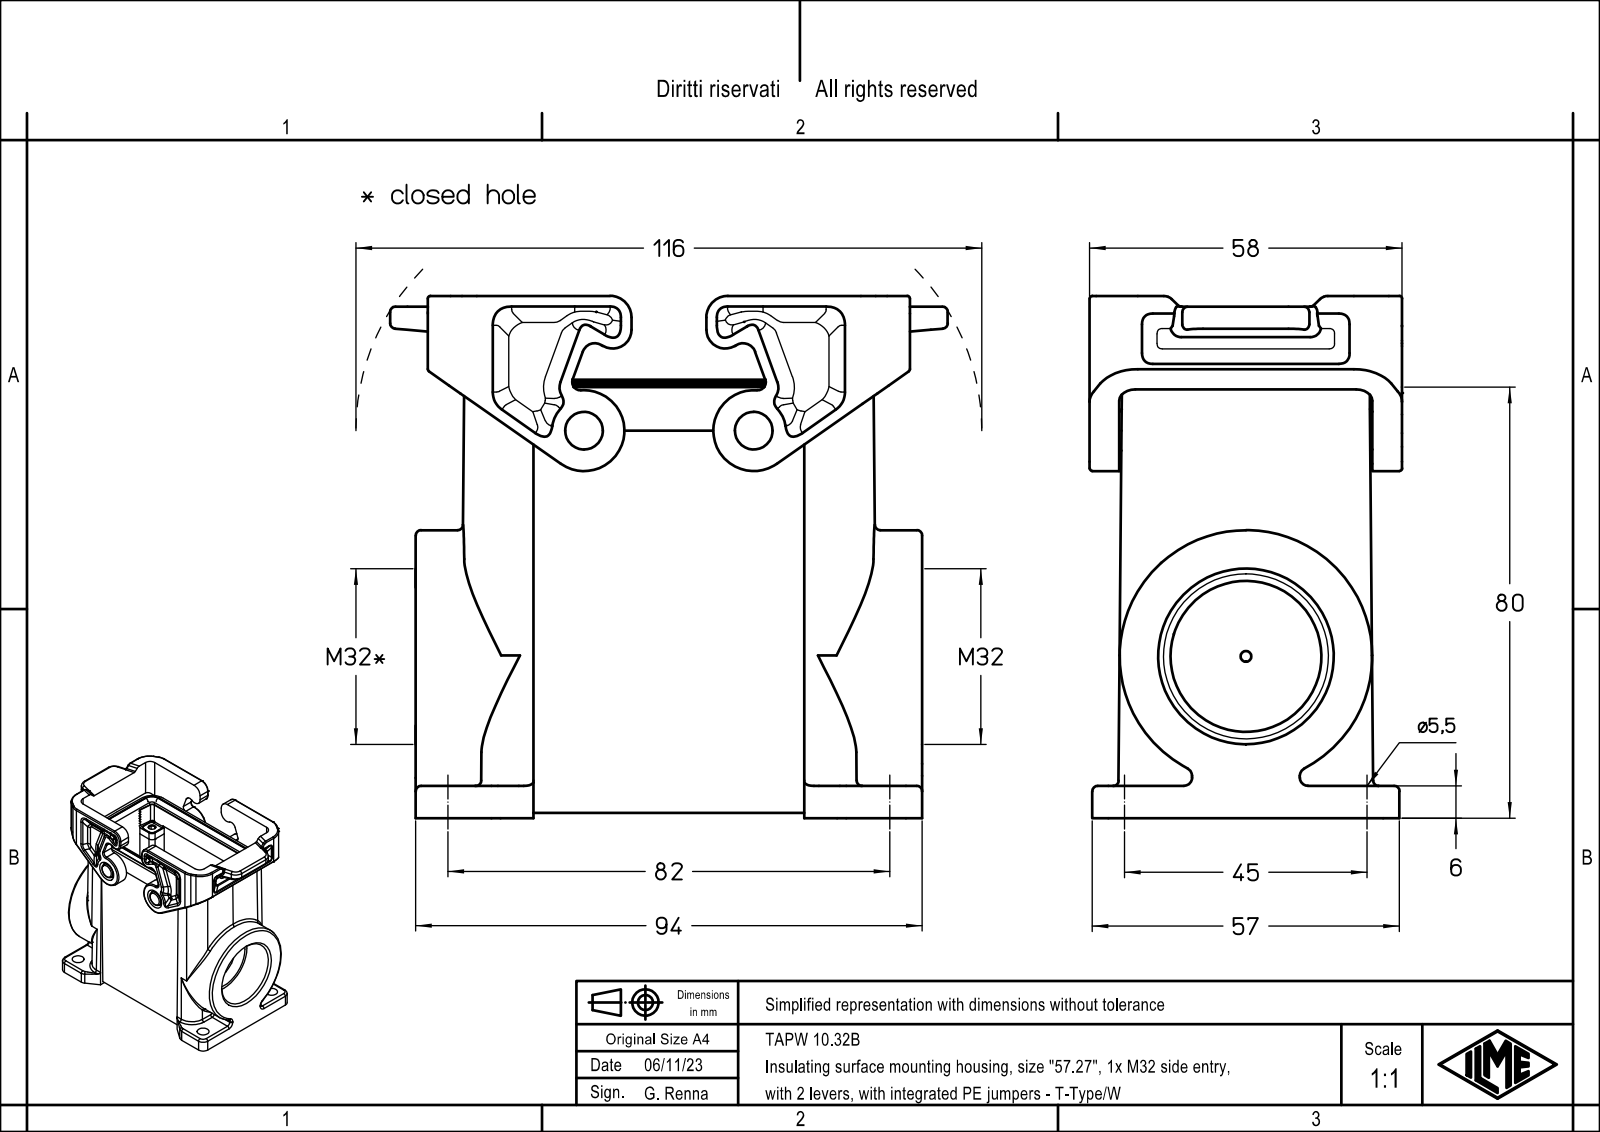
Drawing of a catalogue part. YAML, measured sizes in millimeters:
part_name: "TAPW 10.32B"
step_written_by: "Creo Elements/Direct Modeling 20.1B 02-Apr-2019 (C) Parametric Technology GmbH (AUTOMOTIVE_DESIGN)"
units: millimeters
bodies: {solids: 1, faces: 606, planar: 360, cylindrical: 194, other: 52}
overall_size: [103.5, 96.9, 58]
volume: 172237
surface_area: 63909
round_holes:
  - {diameter: 3.5, count: 4}
  - {diameter: 5.5, count: 4}
  - {diameter: 28, count: 1}
  - {diameter: 30.6, count: 1}
round_bosses_or_shafts:
  - {diameter: 7, count: 2}
  - {diameter: 46.87, count: 1}
partial_cylinders:
  - {radius: 2, count: 20}
  - {radius: 3, count: 20}
  - {radius: 1.5, count: 18}
  - {radius: 1, count: 16}
  - {radius: 1.3, count: 12}
  - {radius: 6, count: 8}
  - {radius: 7, count: 8}
  - {radius: 4, count: 6}
face_to_face_distances: [35.2, 5.5, 5.9, 41.1, 1, 6.5, 11.4, 46.6, 52.5, 5]
hole_center_spacings: [15.4, 38.11, 70.08, 78.27, 27, 45, 57, 63.07]
